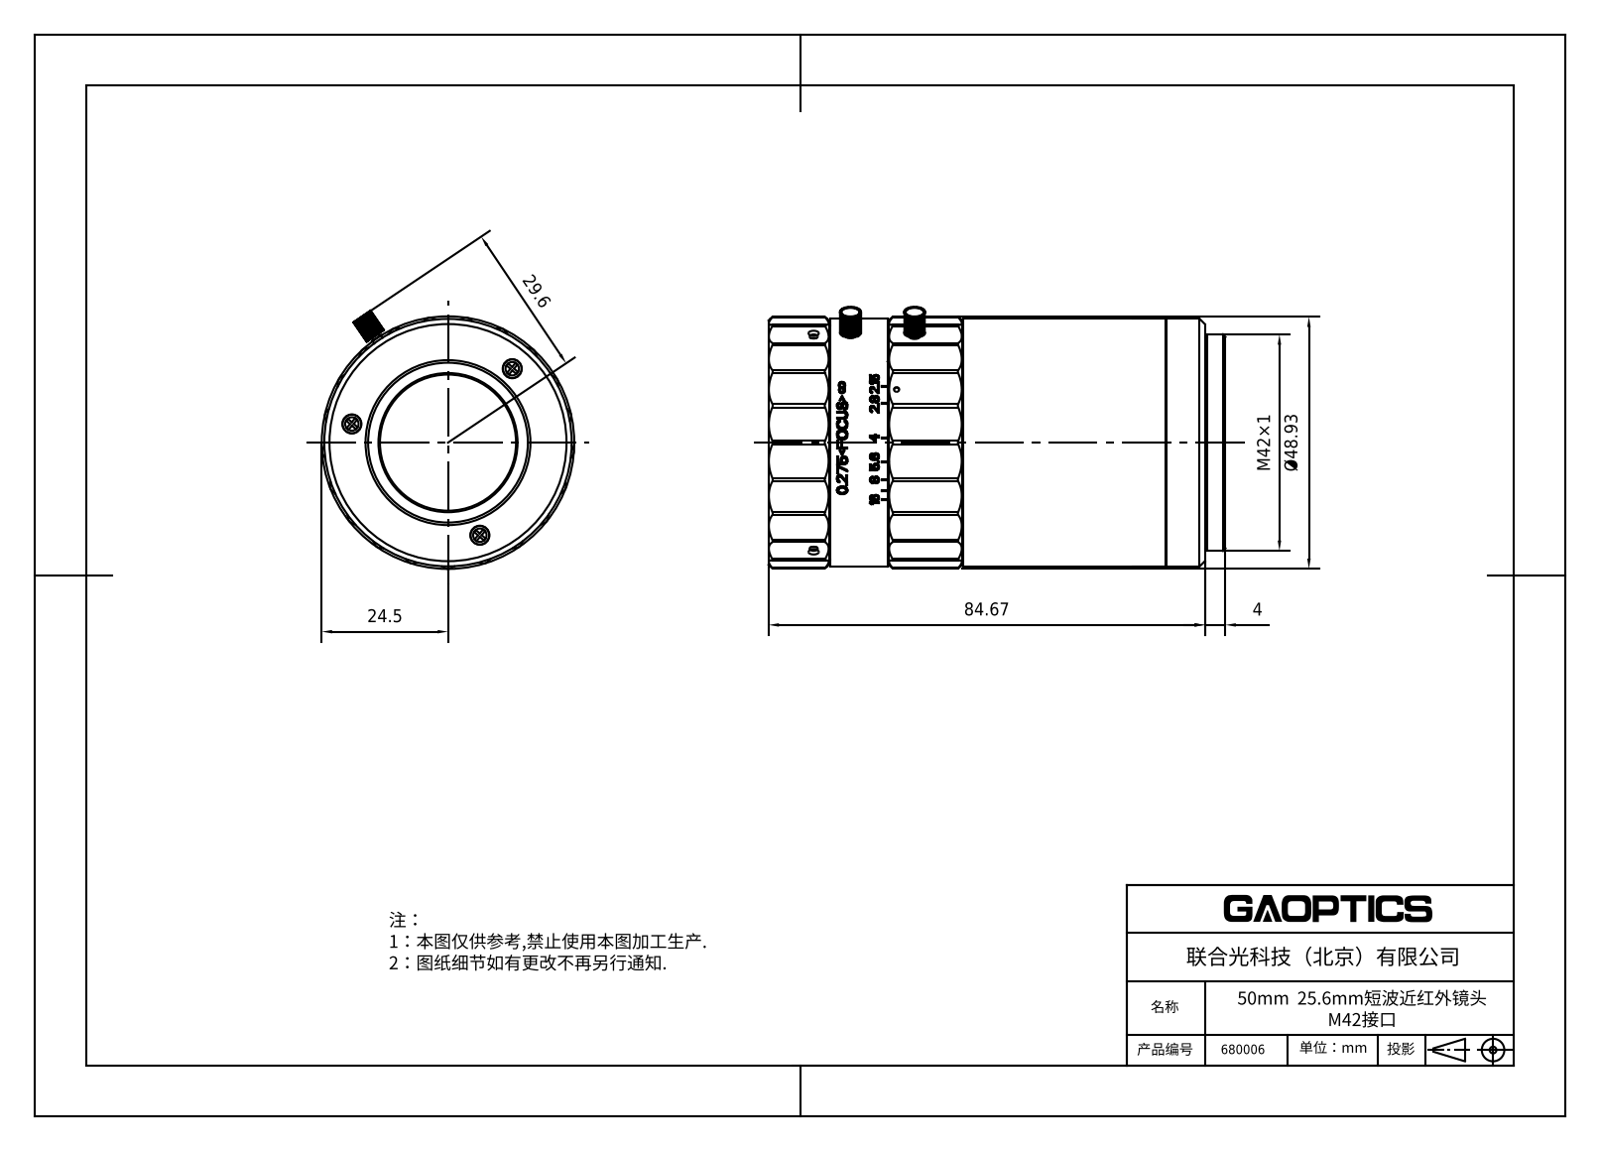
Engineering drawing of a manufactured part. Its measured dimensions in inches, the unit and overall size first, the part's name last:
Units: inches
Overall size (bounding box): 3.253 × 2.077 × 1.923
Round holes (diameter × count): ⌀0.063 ×8, ⌀0.039 ×3, ⌀0.043 ×3, ⌀0.083 ×3, ⌀0.146 ×3, ⌀0.051 ×1, ⌀0.65 ×1, ⌀0.913 ×1, ⌀0.969 ×1, ⌀1.071 ×1, ⌀1.102 ×1, ⌀1.11 ×1
Round bosses / shafts (diameter × count): ⌀0.079 ×5, ⌀0.142 ×3, ⌀0.059 ×2, ⌀1.89 ×1, ⌀1.831 ×1, ⌀1.827 ×1, ⌀1.791 ×1, ⌀1.693 ×1
Partial cylindrical surfaces — rounded edges, fillets, slot ends (radius × count): R0.472 ×30, R0.037 ×26, R0.059 ×4, R0.079 ×2, R0.943 ×1
Main face-to-face distances: 0.236, 2.702, 0.157, 0.138, 0.374, 2.135, 1.997, 1.761, 0.315, 1.576
Hole centre spacings: 0.748, 0.374, 0.657, 0.918, 0.996, 1.296, 1.357, 0.091
Bodies: 0 solids, 2747 faces (1553 planar, 418 cylindrical, 776 other)
Part name (STEP PRODUCT): 680006
STEP written by: SolidWorks 2020 (CONFIG_CONTROL_DESIGN)
